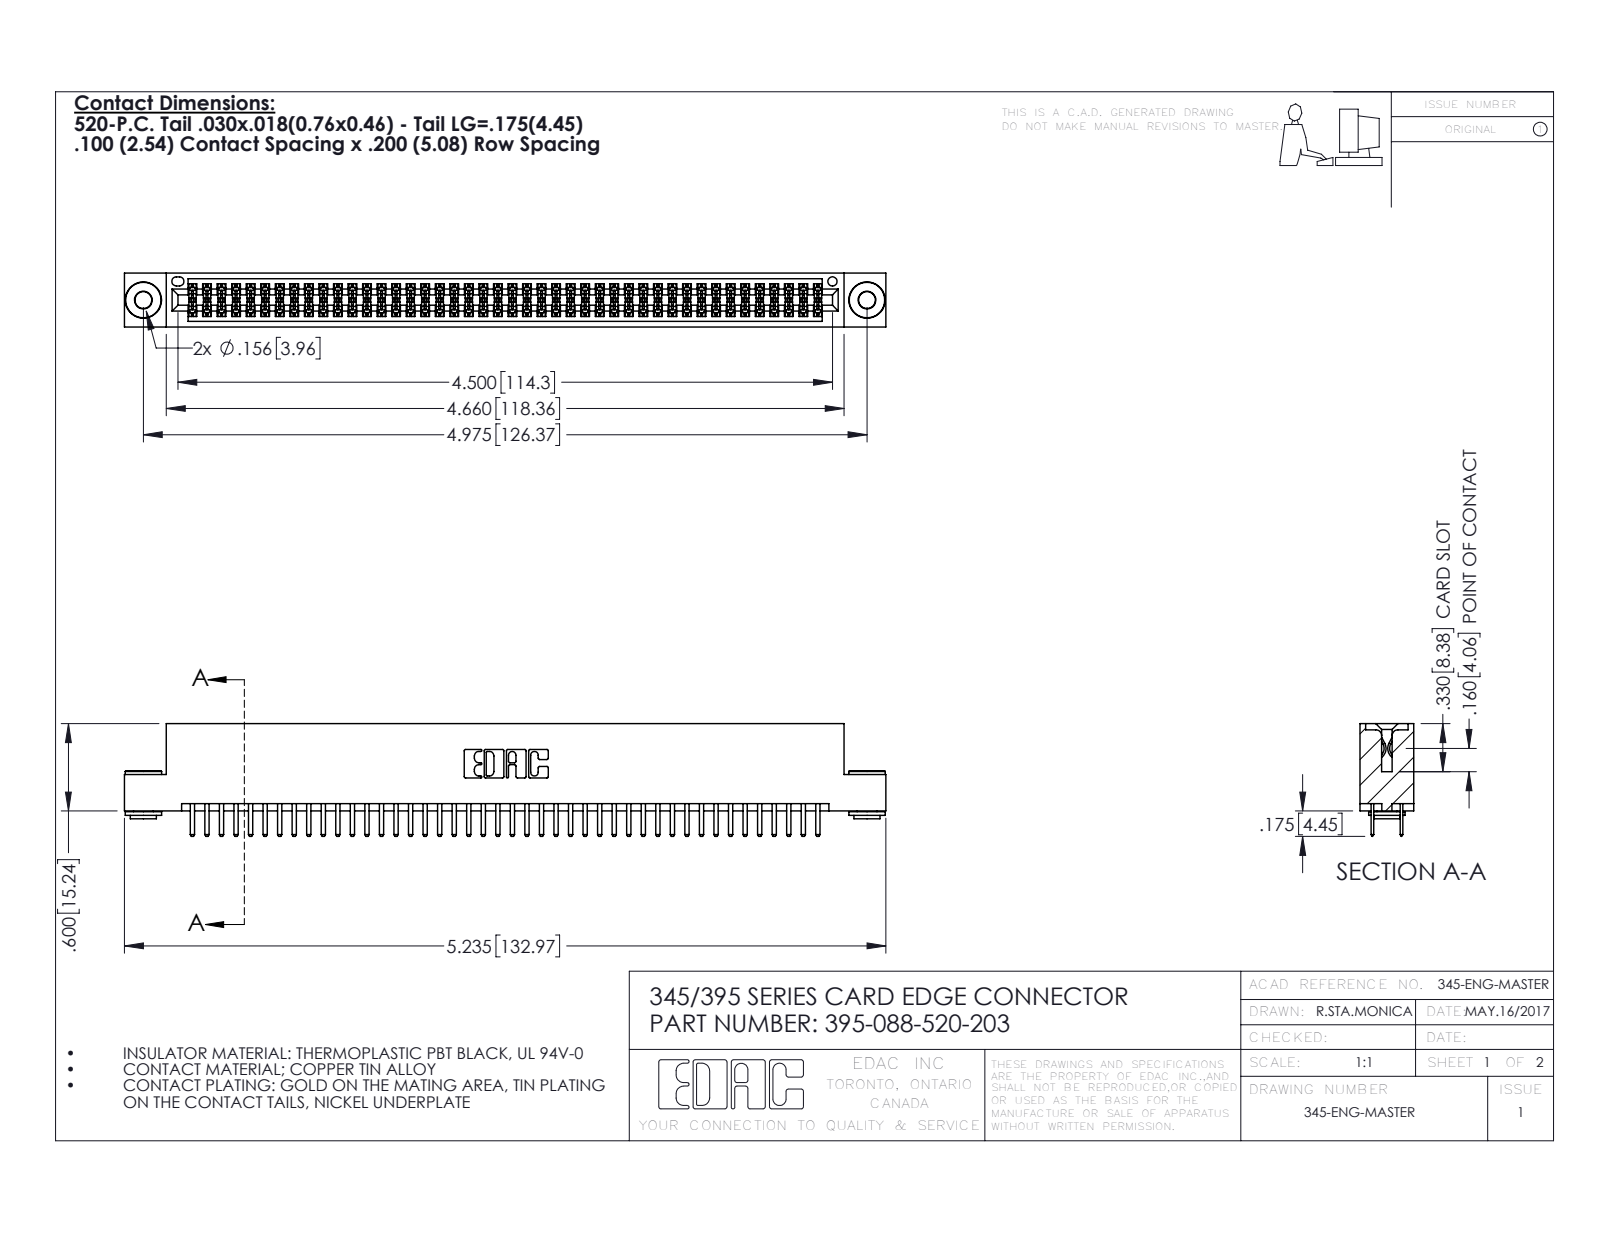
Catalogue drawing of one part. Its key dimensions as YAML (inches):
part_name: "345-250-002_345-250-002-102; 345-292-001_345-293-120; 345 Part_Flush Mounting Lugs - 0.156 Dia-TH; 395-088-520-203"
step_written_by: "SolidWorks 2016 (CONFIG_CONTROL_DESIGN)"
units: inches
bodies: {solids: 91, faces: 4916, planar: 3170, cylindrical: 1738, other: 8}
overall_size: [5.235, 0.775, 0.37]
volume: 0.788
surface_area: 29.84
round_holes:
  - {diameter: 0.116, count: 2}
  - {diameter: 0.156, count: 2}
  - {diameter: 0.064, count: 1}
round_bosses_or_shafts:
  - {diameter: 0.25, count: 2}
  - {diameter: 0.18, count: 2}
  - {diameter: 0.136, count: 2}
partial_cylinders:
  - {radius: 0.006, count: 132}
  - {radius: 0.01, count: 92}
  - {radius: 0.01, count: 22}
  - {radius: 0.007, count: 6}
  - {radius: 0.031, count: 6}
  - {radius: 0.026, count: 3}
  - {radius: 0.014, count: 2}
  - {radius: 0.019, count: 2}
face_to_face_distances: [0.072, 0.298, 0.2, 0.37, 0.025, 0.098, 0.272, 0.225, 0.022, 0.072]
hole_center_spacings: [0.27, 4.739, 4.975]
